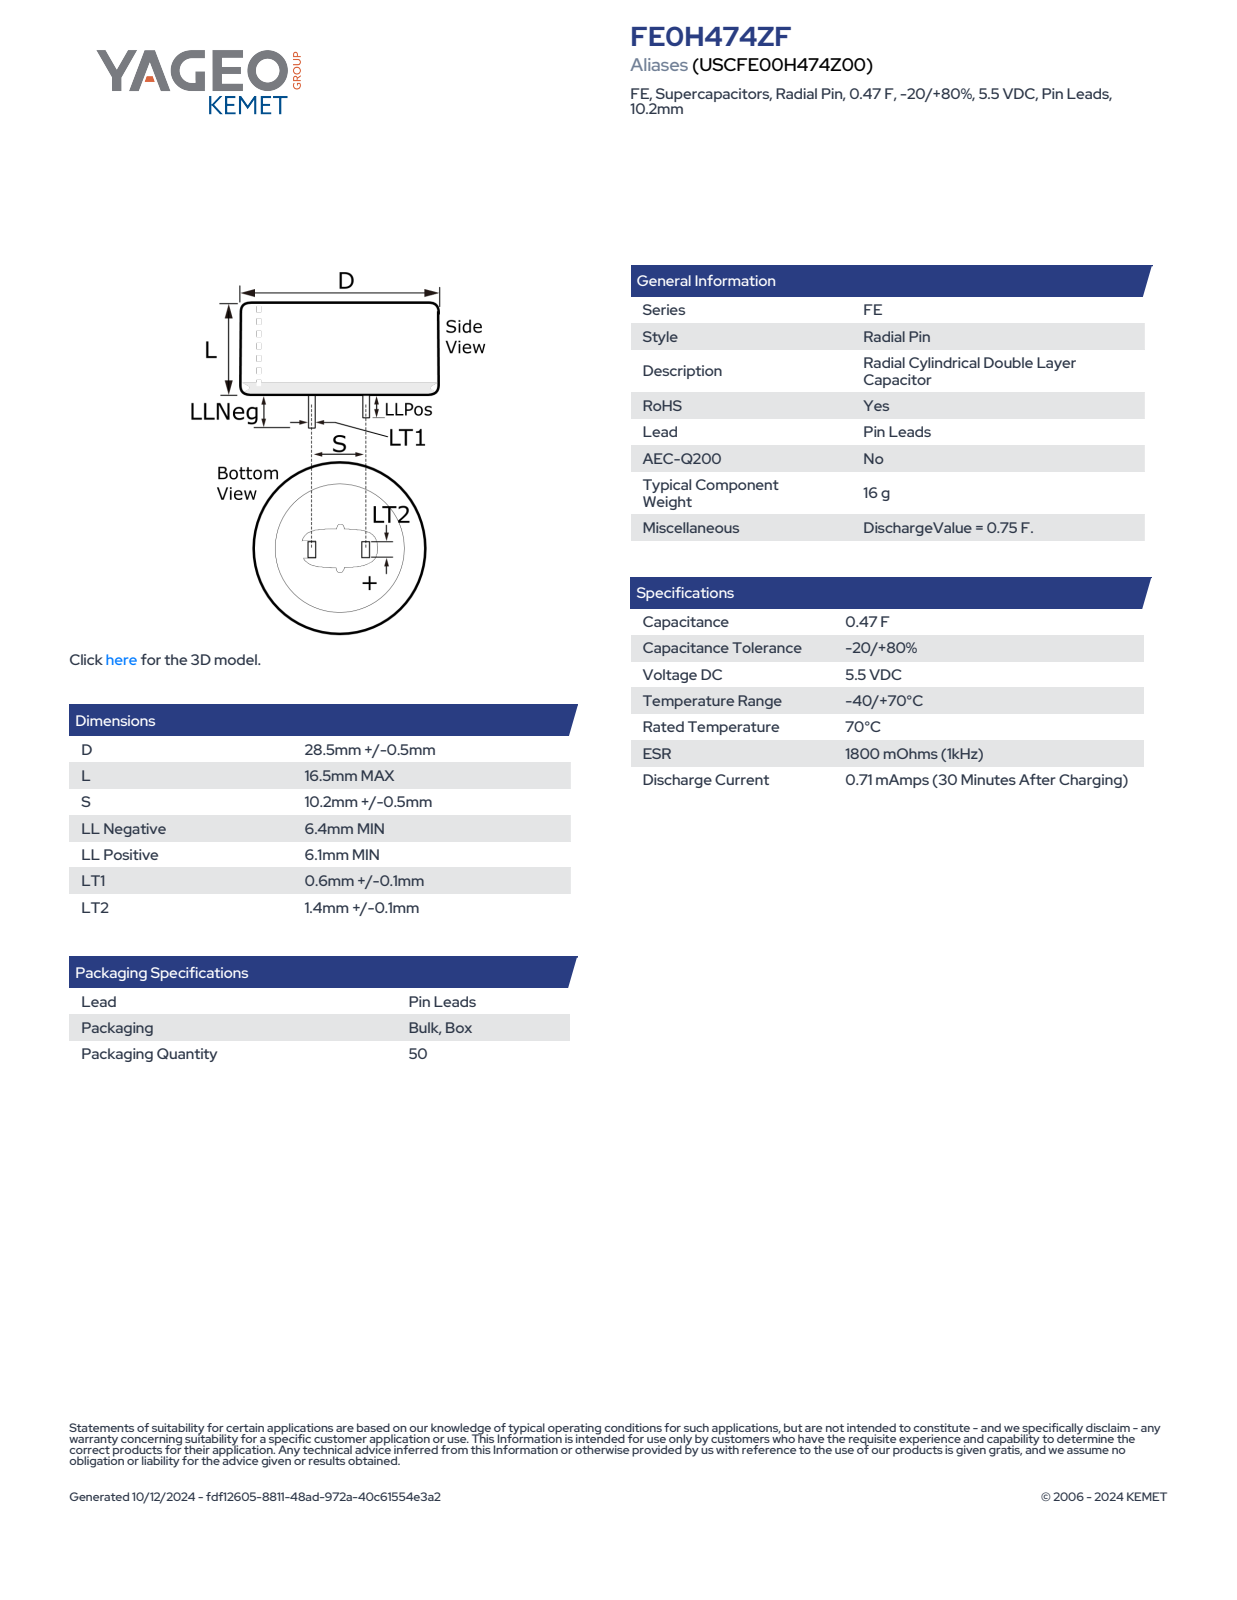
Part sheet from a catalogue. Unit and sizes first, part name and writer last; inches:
Units: inches
Overall size (bounding box): 1.142 × 1.142 × 0.902
Round bosses / shafts (diameter × count): ⌀1.142 ×1
Partial cylindrical surfaces — rounded edges, fillets, slot ends (radius × count): R0.571 ×1
Main face-to-face distances: 0.65, 0.028, 0.402, 0.429, 0.374, 0.059, 0.252, 0.902, 0.24, 0.89
Volume: 0.663 in³ · Surface area: 4.334 in²
Bodies: 1 solid, 78 faces (70 planar, 4 cylindrical, 4 other)
Part name (STEP PRODUCT): CDR_LPLLN_D29L16.5S10.2LLNEG6.4LLPOS6.1LT10.7LT21.5
STEP written by: SolidWorks 2014 (AUTOMOTIVE_DESIGN)
